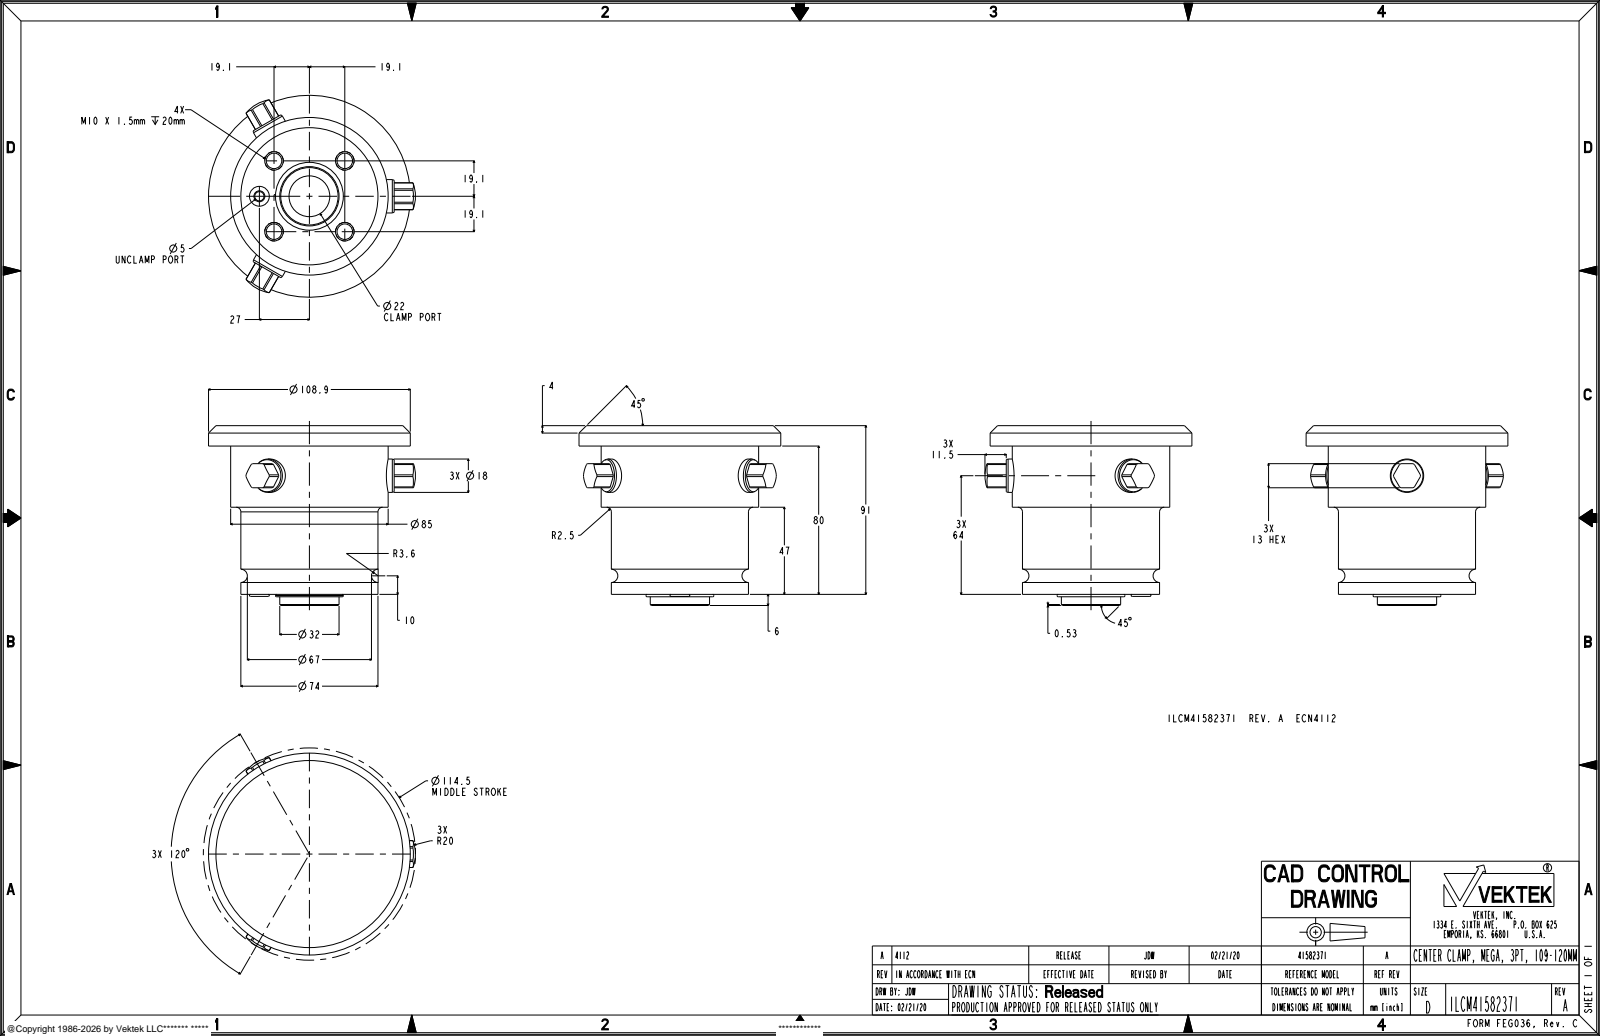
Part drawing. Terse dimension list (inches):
name: ILCM41582371
written by: PRO/ENGINEER BY PARAMETRIC TECHNOLOGY CORPORATION, 2013320 (AUTOMOTIVE_DESIGN)
unit: in
bodies: 1 solid, 158 faces (46 planar, 64 cylindrical, 48 other)
size: 4.398 × 4.287 × 3.819
volume: 29.78 in³; area: 81.79 in²
holes: 4× ⌀0.33, 3× ⌀0.709, 1× ⌀0.197, 1× ⌀0.866
bosses: 4× ⌀0.394, 1× ⌀4.287, 1× ⌀3.346, 1× ⌀2.913, 1× ⌀1.441, 1× ⌀1.26
rounds: 3× R0.285
face distances: 0.433, 3.15, 3.583, 1.85, 1.299, 1.732, 0.148, 0.118, 0.512, 0.886
hole spacings: 1.063, 1.504, 0.814, 1.965, 2.127, 1.063
